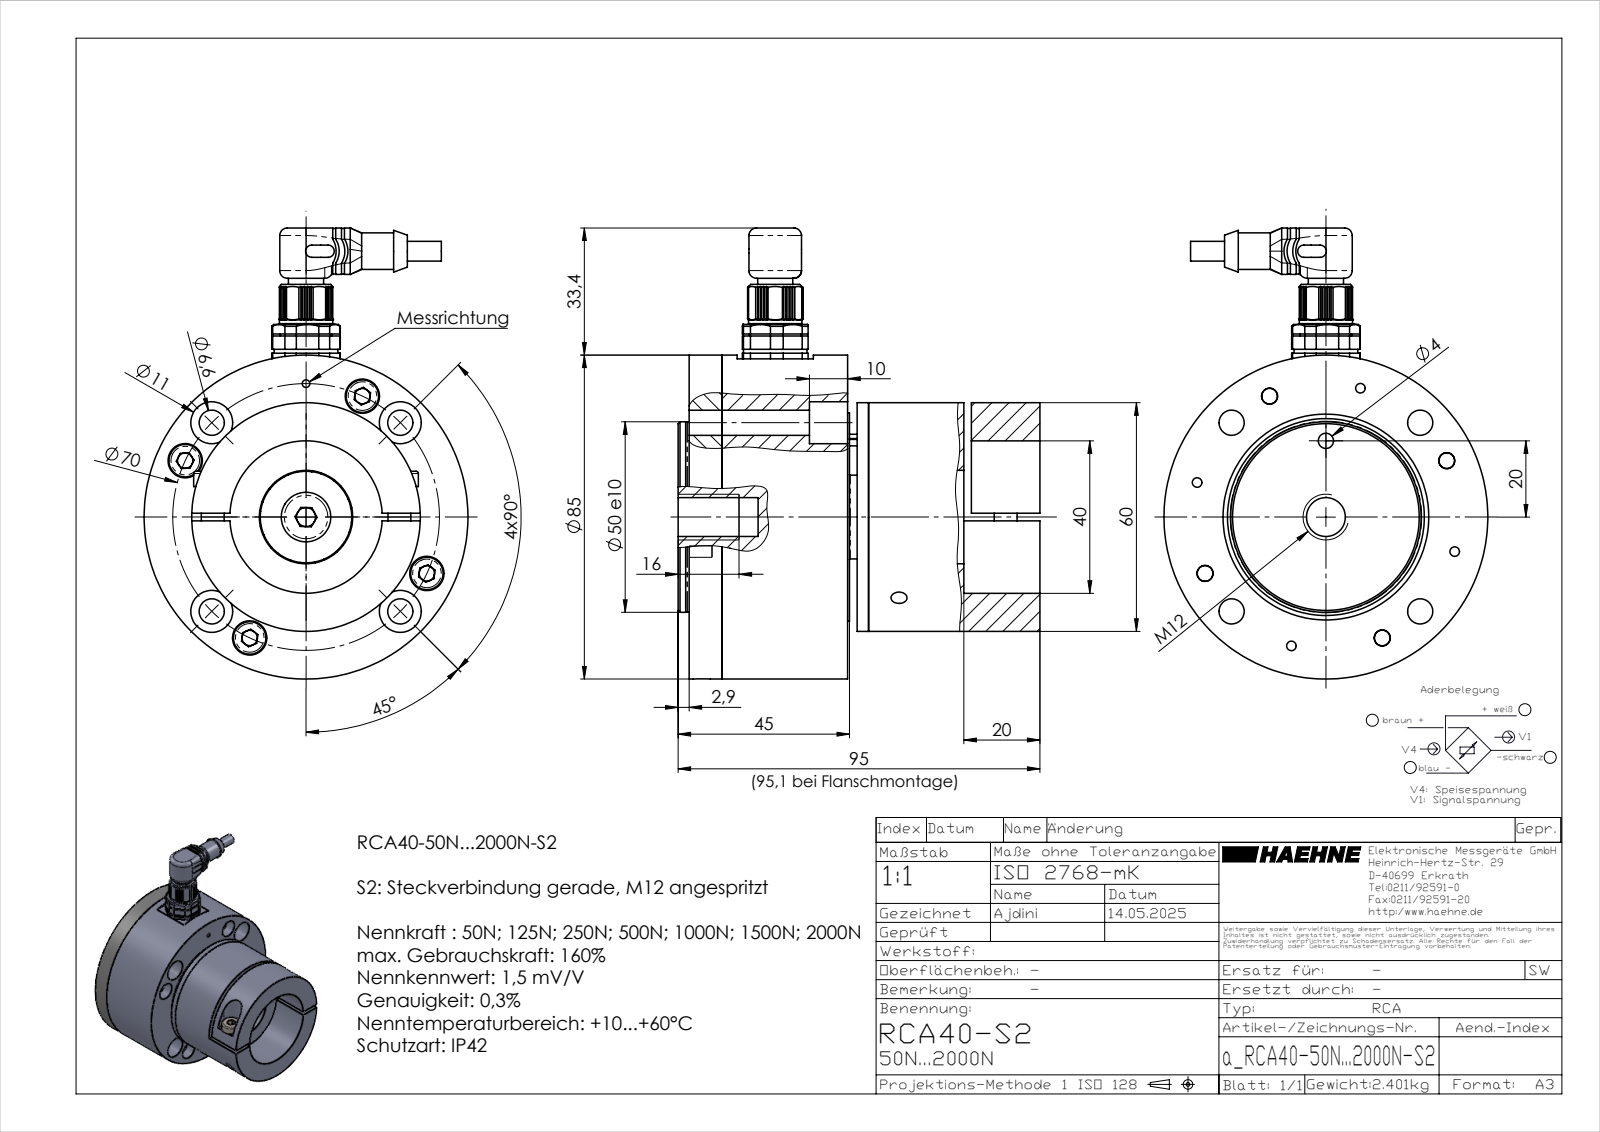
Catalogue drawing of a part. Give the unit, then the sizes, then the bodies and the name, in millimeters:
Units: millimetres
Overall size (bounding box): 118.35 × 95.1 × 85
Round holes (diameter × count): ⌀3.4 ×9, ⌀2.5 ×8, ⌀6.6 ×6, ⌀4.2 ×5, ⌀11 ×5, ⌀1.1 ×4, ⌀1.15 ×4, ⌀1.6 ×4, ⌀1.85 ×4, ⌀4 ×4, ⌀5.3 ×4, ⌀9 ×4
Round bosses / shafts (diameter × count): ⌀3 ×9, ⌀5.7 ×8, ⌀8.5 ×4, ⌀5 ×4, ⌀1.8 ×4, ⌀1.55 ×4, ⌀1.5 ×4, ⌀1 ×4
Partial cylindrical surfaces — rounded edges, fillets, slot ends (radius × count): R0.2 ×16, R0.3 ×9, R0.4 ×4, R0.53 ×4, R1 ×4, R1.27 ×4, R6 ×4, R1.6 ×2
Main face-to-face distances: 3, 8.6, 47.1, 2, 11.6, 30, 35.5, 45, 50.1, 38.5
Hole centre spacings: 35, 49.5, 24.78, 25.2, 32.8, 51.14, 56.46, 2.5
Volume: 351 920 mm³ · Surface area: 112 279 mm²
Bodies: 53 solids, 1226 faces (662 planar, 295 cylindrical, 269 other)
Part name (STEP PRODUCT): inafag_1203-tvh_7zkvytp7yxkimpdvw8sj0b5w4_13; Washer DIN 9021 - 8.4_Washer DIN 9021 - 8.4; anf_RCA30 Scheibe A; inafag_1203-tvh_7zkvytp7yxkimpdvw8sj0b5w4_08 (+8 more)
STEP written by: SolidWorks 2023 (AUTOMOTIVE_DESIGN)
